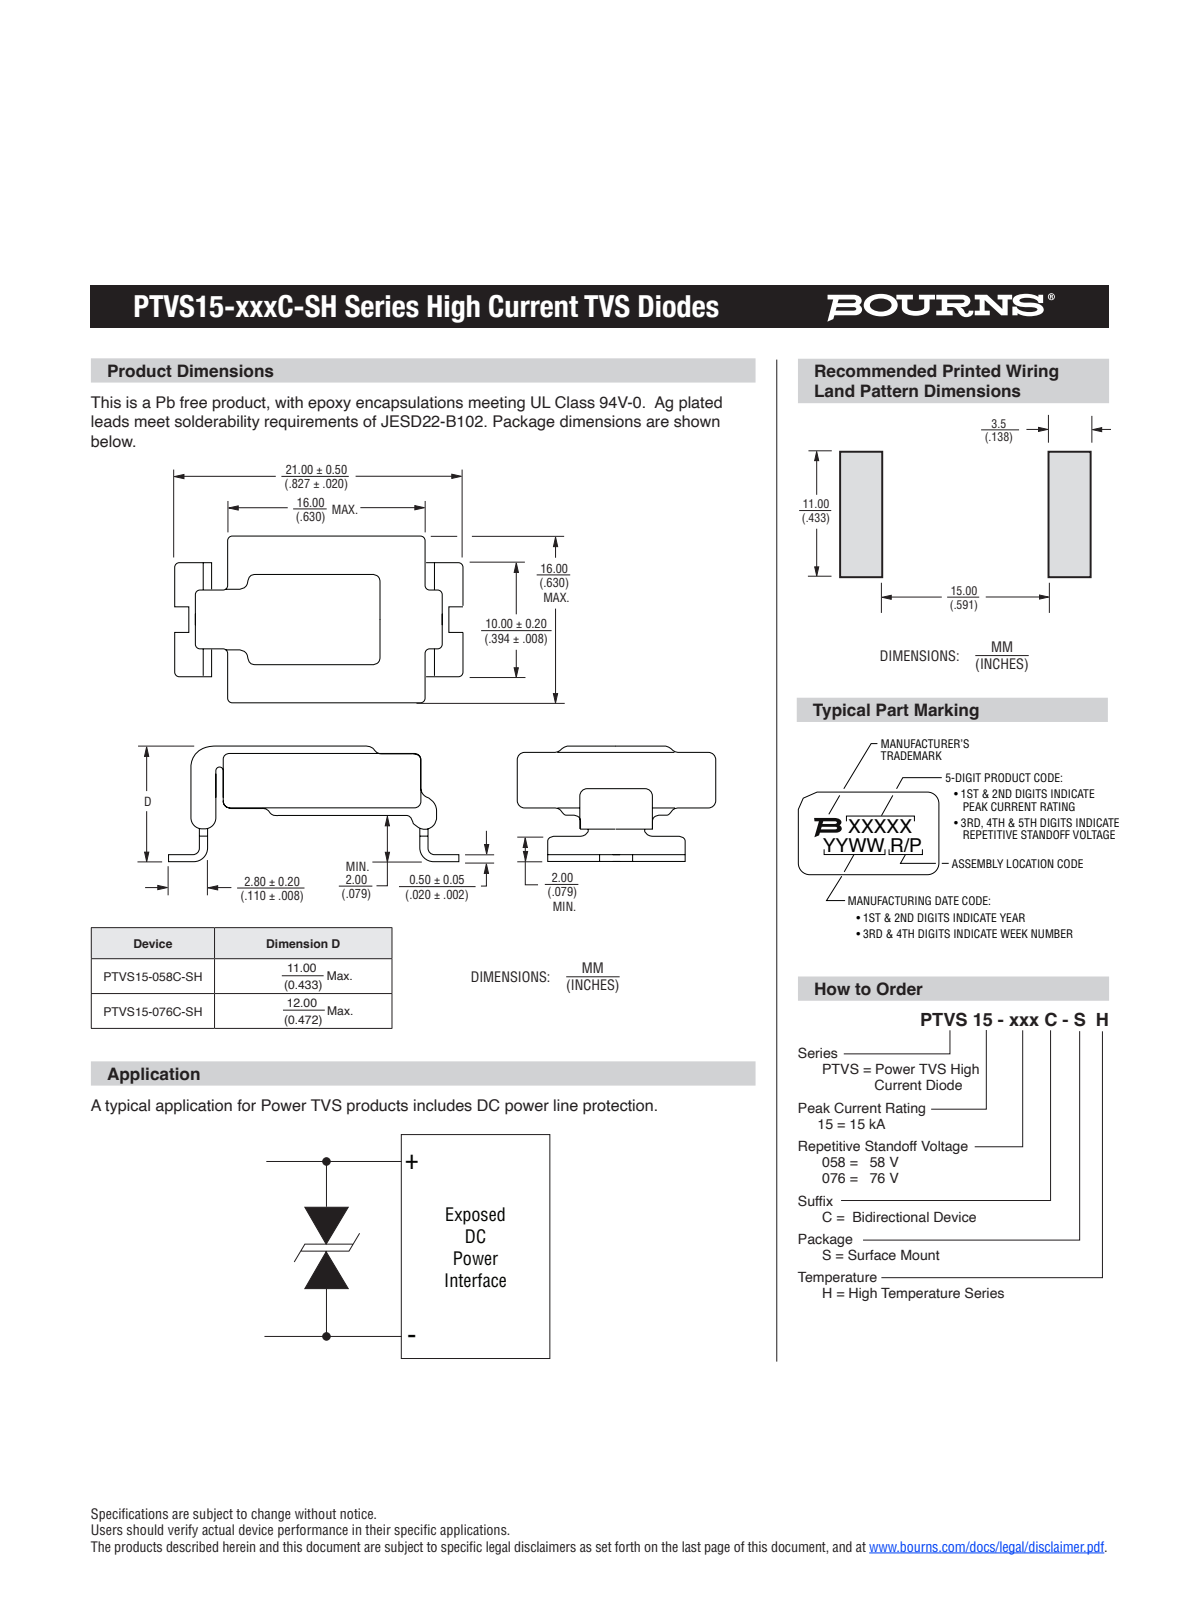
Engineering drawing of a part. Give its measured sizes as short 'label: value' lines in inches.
name: PTVS15-0xxC-SH
written by: SolidWorks 2012 (CONFIG_CONTROL_DESIGN)
unit: in
bodies: 3 solids, 204 faces (58 planar, 86 cylindrical, 60 other)
size: 0.828 × 0.565 × 0.393
volume: 0.074 in³; area: 1.575 in²
rounds: 43× R0.01, 20× R0.02, 5× R0.03, 3× R0.031, 1× R0.004, 1× R0.021, 1× R0.022, 1× R0.028
face distances: 0.025, 0.209, 0.024, 0.184, 0.565, 0.234, 0.563, 0.047, 0.654, 0.631
